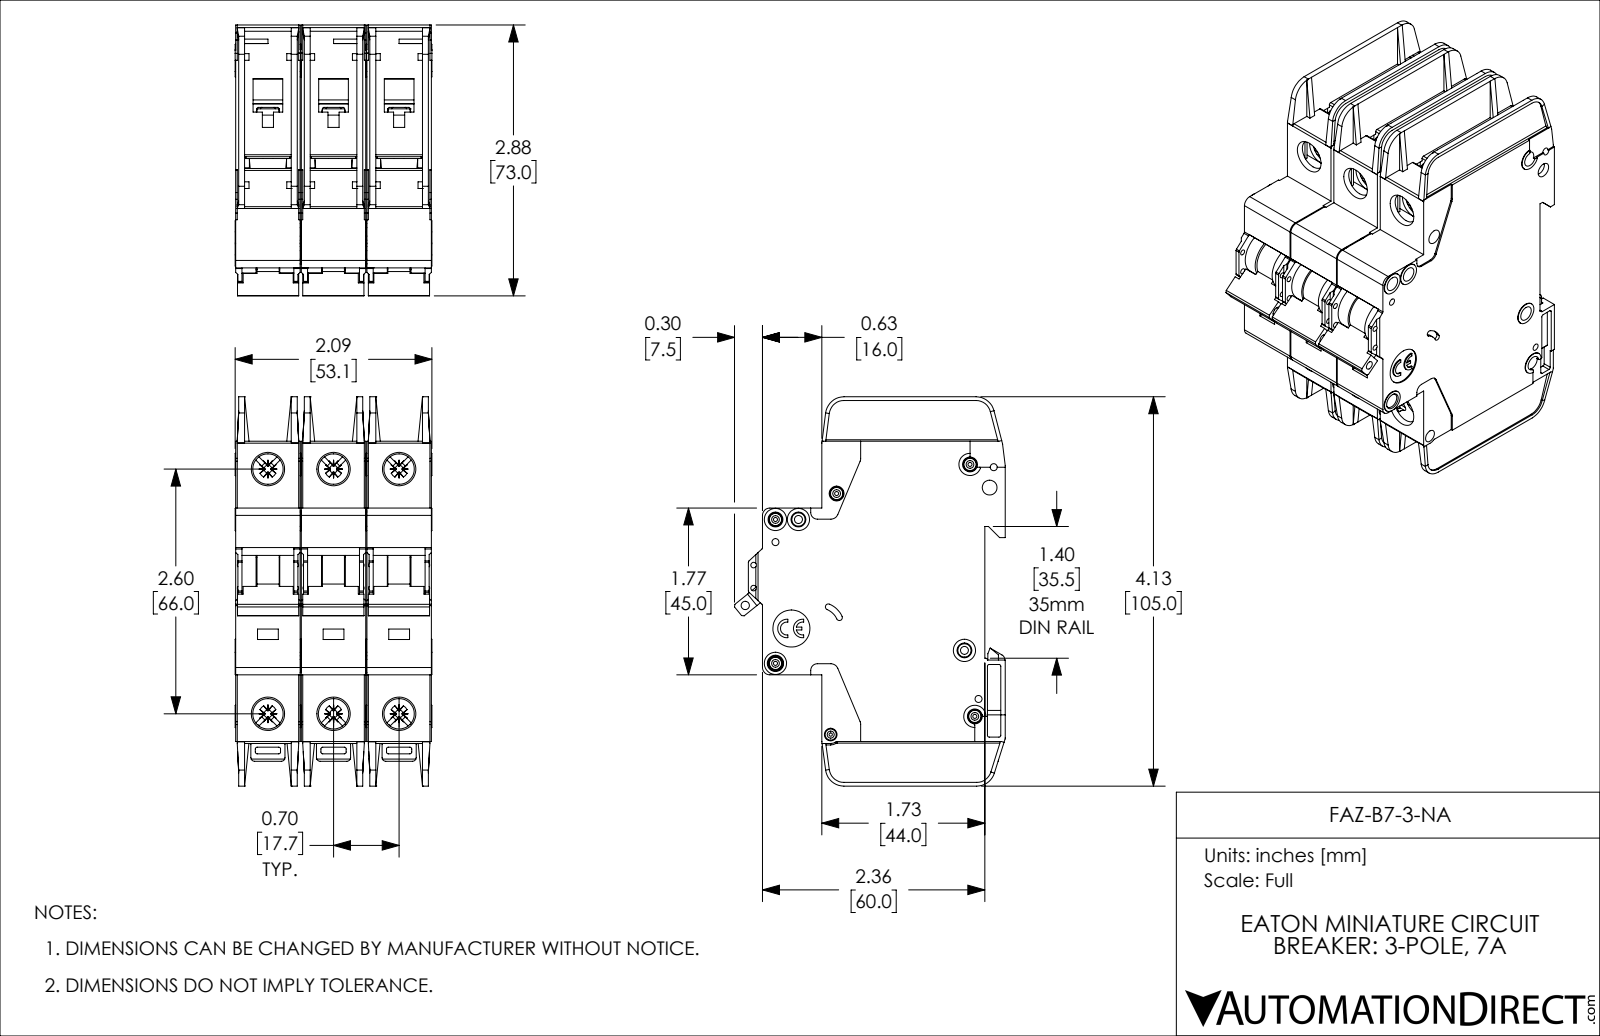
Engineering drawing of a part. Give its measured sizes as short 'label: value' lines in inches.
name: FAZ-B7-3-NA
written by: SolidWorks 2019 (AUTOMOTIVE_DESIGN)
unit: in
bodies: 3 solids, 3381 faces (2013 planar, 1071 cylindrical, 297 other)
size: 4.134 × 2.876 × 2.091
volume: 14.05 in³; area: 123 in²
holes: 8× ⌀0.157, 6× ⌀0.323, 5× ⌀0.043, 4× ⌀0.075, 2× ⌀0.059, 2× ⌀0.085, 1× ⌀0.035, 1× ⌀0.089, 1× ⌀0.098, 1× ⌀0.134, 1× ⌀0.394
bosses: 5× ⌀0.13, 4× ⌀0.236, 4× ⌀0.118, 3× ⌀0.098
rounds: 72× R0.02, 30× R0.016, 18× R0.039, 12× R0.043, 12× R0.079, 6× R0.008, 6× R0.01, 6× R0.028
face distances: 0.697, 0.047, 1.394, 0.685, 0.591, 1.382, 0.744, 0.65, 0.106, 0.094
hole spacings: 0.697, 2.69, 2.598, 0.244, 0.537, 0.87, 1.394, 2.948
